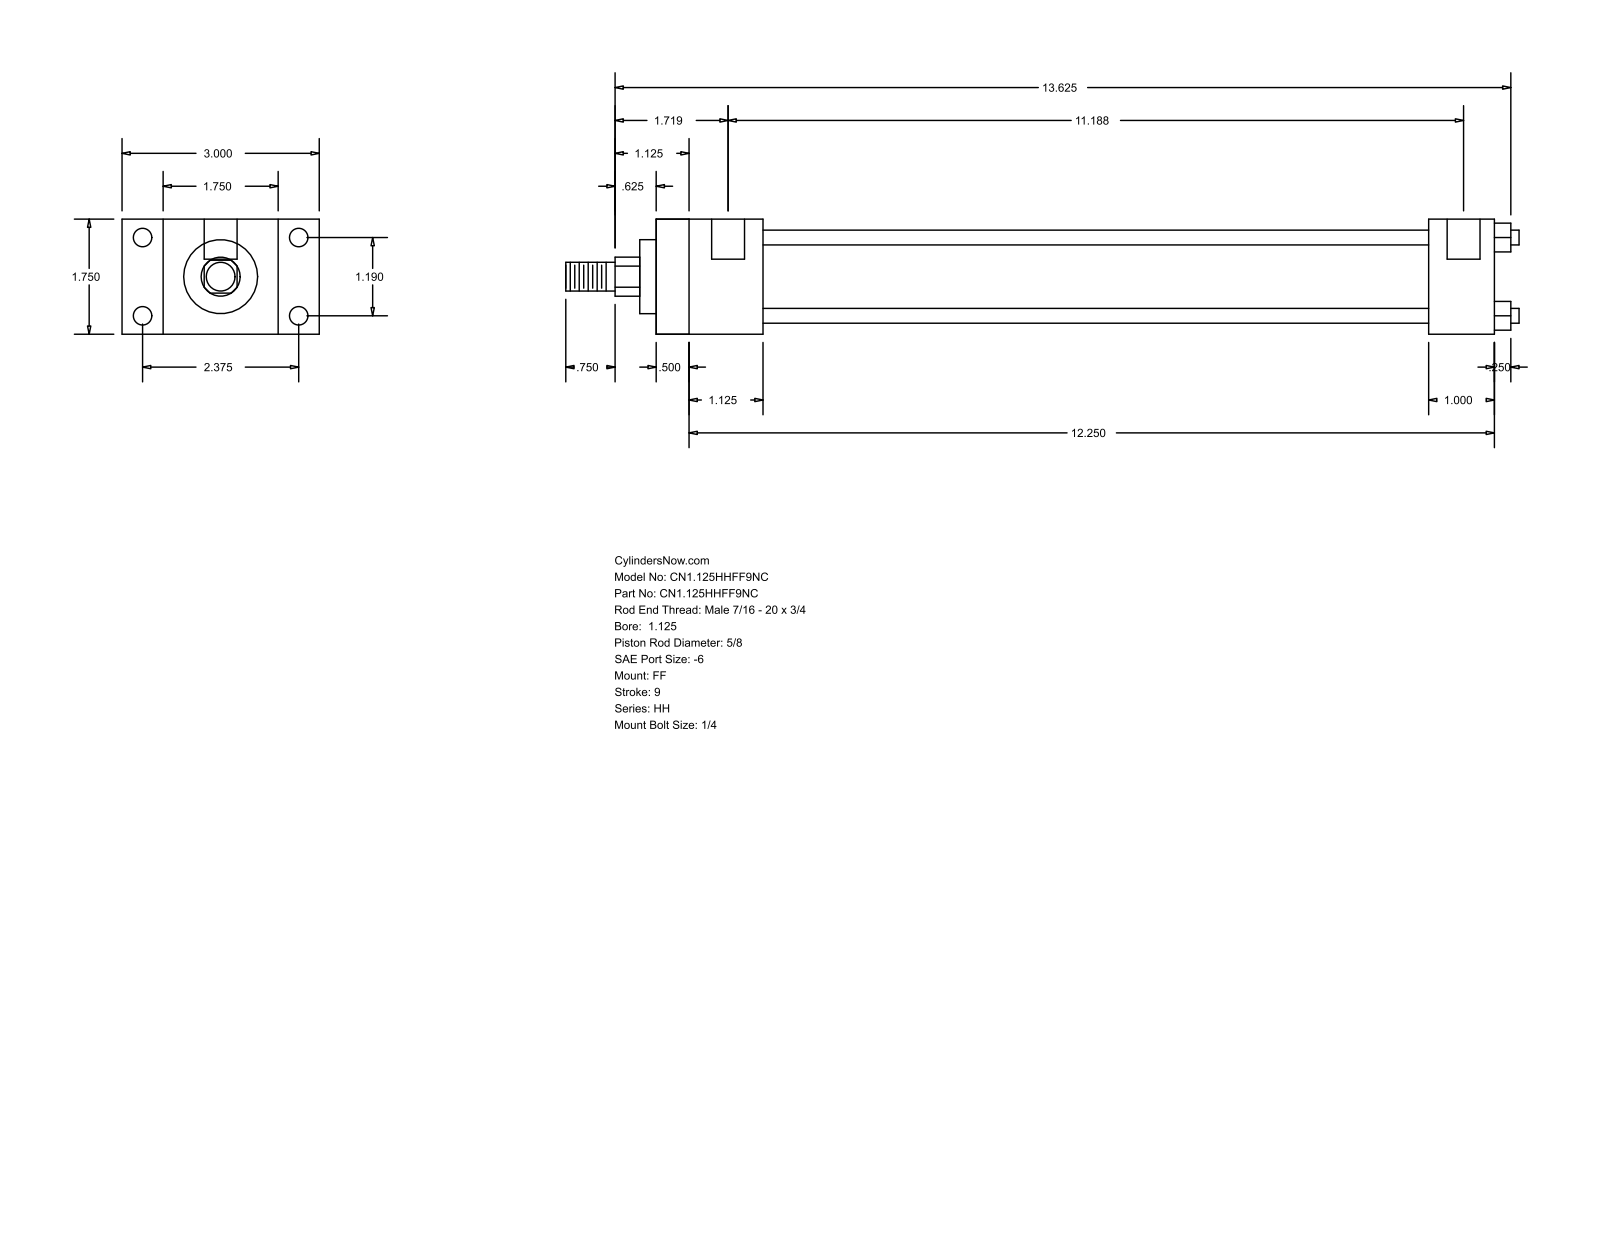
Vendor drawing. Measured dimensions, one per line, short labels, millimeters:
name: HH_FF__0112_0.625
written by: GSSL Pune (CONFIG_CONTROL_DESIGN)
unit: mm
bodies: 0 solids, 92 faces (64 planar, 28 cylindrical, 0 other)
size: 368.3 × 76.2 × 44.45
holes: 4× ⌀5.56, 4× ⌀7.14, 2× ⌀12.7
bosses: 4× ⌀5.71, 1× ⌀34.92, 1× ⌀28.57, 1× ⌀15.88, 1× ⌀11.11
rounds: 1× R7.54
face distances: 44.46, 323.85, 15.87, 12.69, 311.16, 28.58, 60.33, 41.27, 298.44, 285.75
hole spacings: 30.22, 60.32, 67.47, 280.99, 3.17, 284.16
